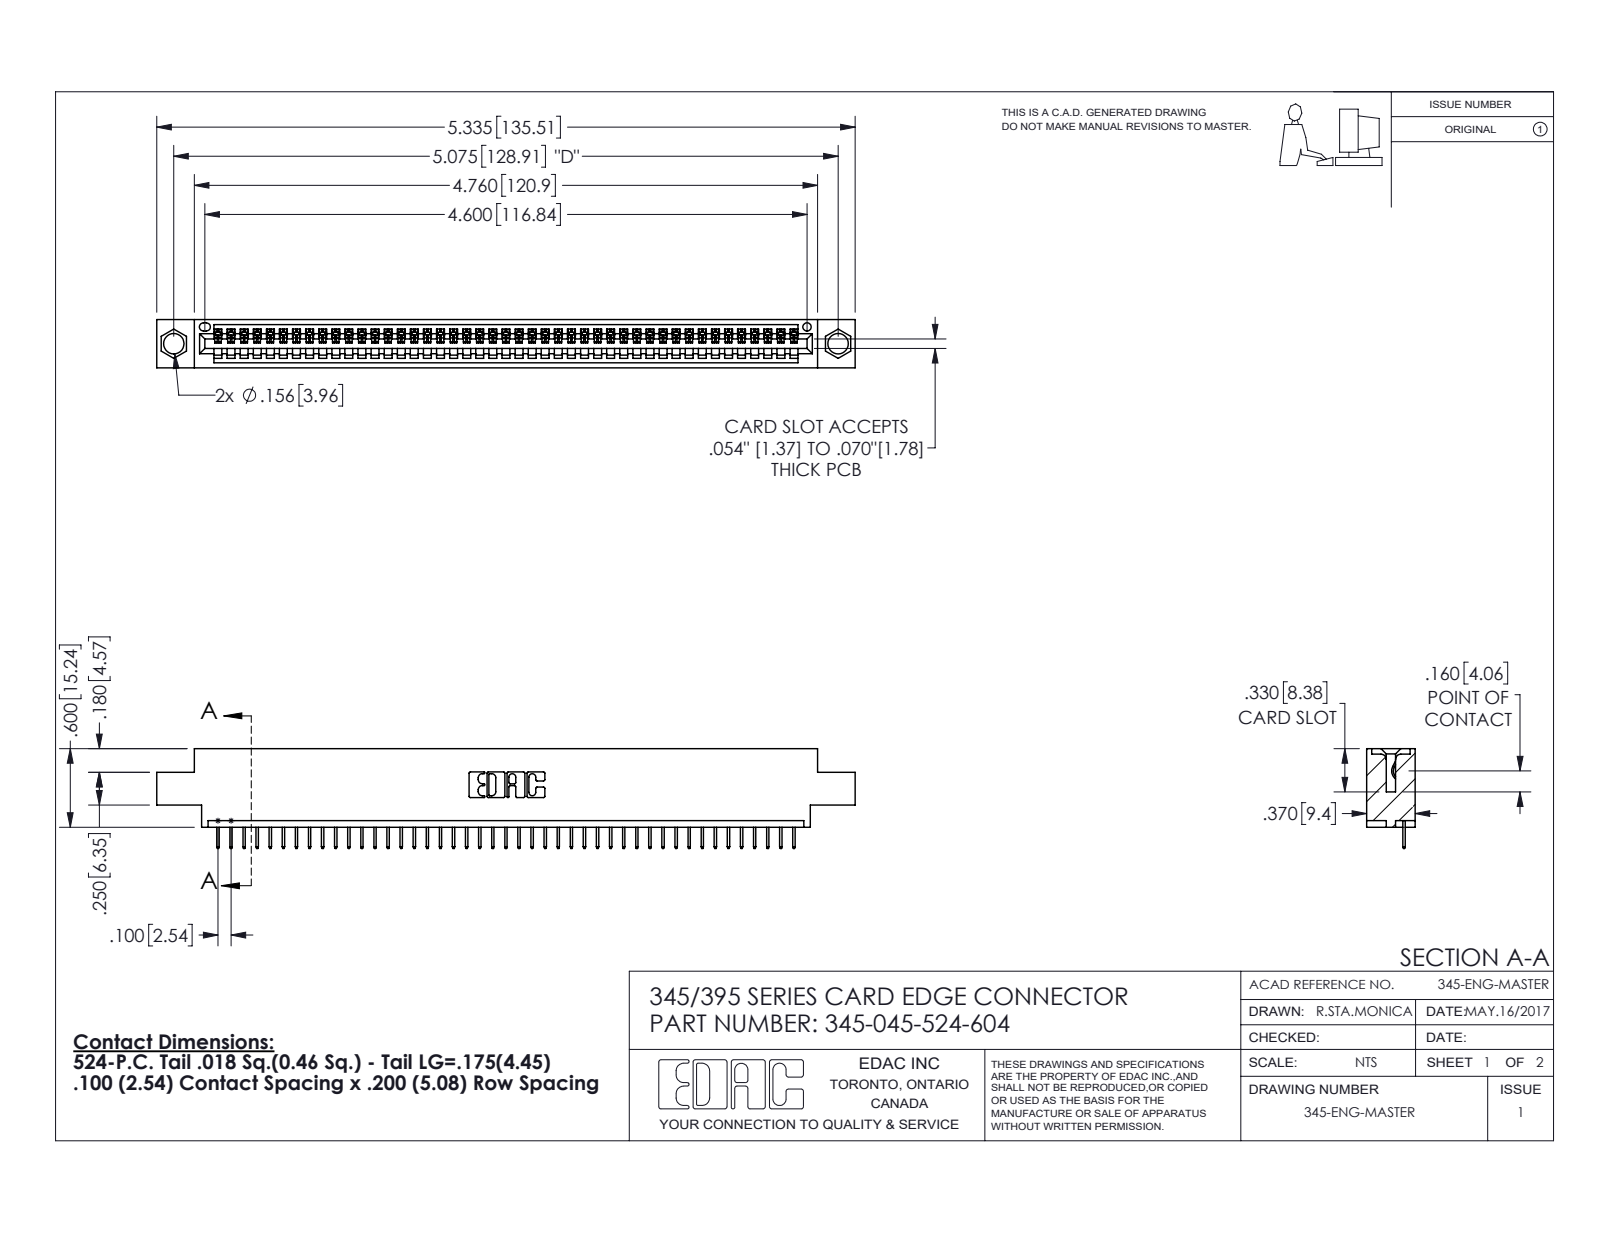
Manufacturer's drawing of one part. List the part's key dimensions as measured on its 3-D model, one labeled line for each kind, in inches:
Part name (STEP PRODUCT): 345 Part_0.170 Offset - 0.156 Dia-TH; 345-045-524-604; 345-292-001_345-293-124
STEP written by: SolidWorks 2016 (CONFIG_CONTROL_DESIGN)
Units: inches
Bodies: 46 solids, 2920 faces (2154 planar, 766 cylindrical, 0 other)
Overall size (bounding box): 5.335 × 0.762 × 0.37
Volume: 0.764 in³ · Surface area: 24.86 in²
Round holes (diameter × count): ⌀0.156 ×2, ⌀0.064 ×1
Partial cylindrical surfaces — rounded edges, fillets, slot ends (radius × count): R0.006 ×90, R0.01 ×22, R0.007 ×6, R0.031 ×6, R0.026 ×3, R0.031 ×2, R0.04 ×2, R0.014 ×1
Main face-to-face distances: 0.072, 0.298, 0.37, 0.2, 0.098, 0.272, 0.025, 0.225, 0.072, 0.175
Hole centre spacings: 0.27, 4.839, 5.075
